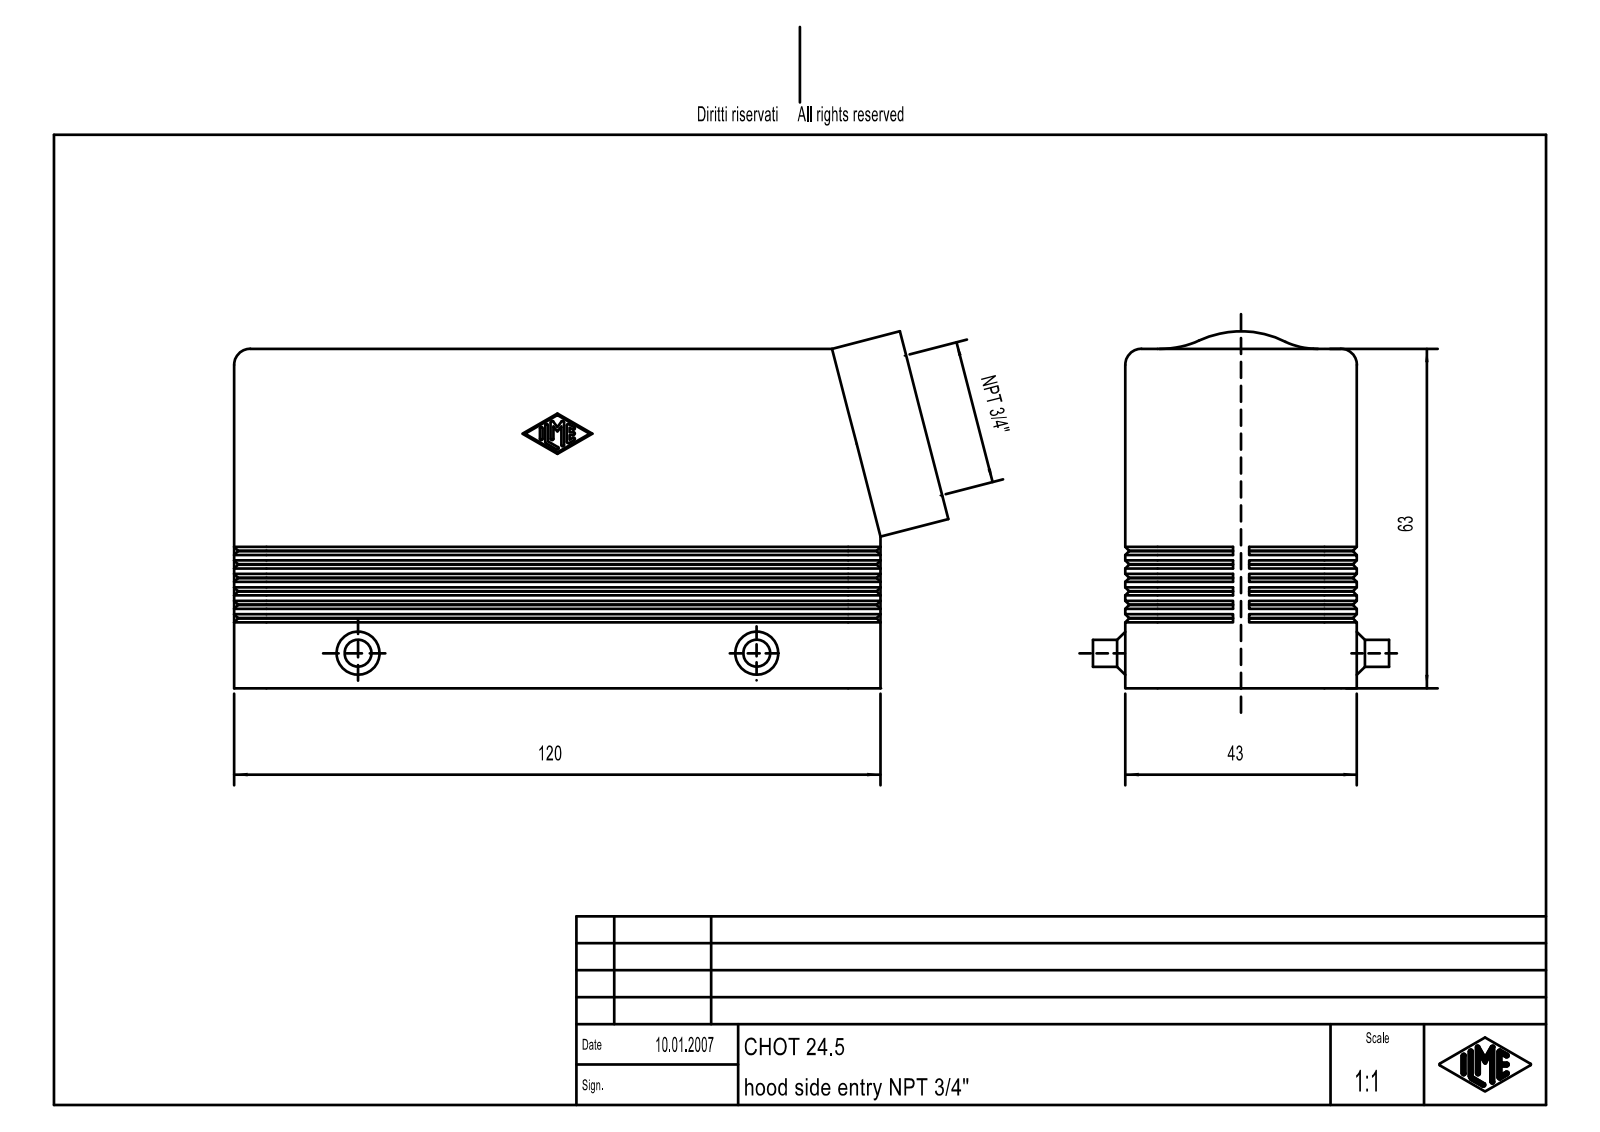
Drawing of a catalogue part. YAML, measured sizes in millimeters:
part_name: "MSBO8107"
step_written_by: "Creo Elements/Direct Modeling 18.0B 02-Dec-2011 (C) Parametric Technology GmbH (AUTOMOTIVE_DESIGN)"
units: millimeters
bodies: {solids: 1, faces: 405, planar: 218, cylindrical: 109, other: 78}
overall_size: [132.59, 66.25, 55]
volume: 89288
surface_area: 50463
round_holes:
  - {diameter: 4, count: 4}
  - {diameter: 2.46, count: 3}
  - {diameter: 2.46, count: 1}
round_bosses_or_shafts:
  - {diameter: 5, count: 2}
  - {diameter: 27.45, count: 1}
partial_cylinders:
  - {radius: 0.25, count: 14}
  - {radius: 3, count: 7}
  - {radius: 2, count: 4}
  - {radius: 5.3, count: 4}
  - {radius: 6, count: 4}
  - {radius: 12.39, count: 1}
face_to_face_distances: [3, 40, 37, 43, 8.5, 11.5, 1.77, 5.3, 105.5, 29.34]
hole_center_spacings: [27, 104, 107.45]
